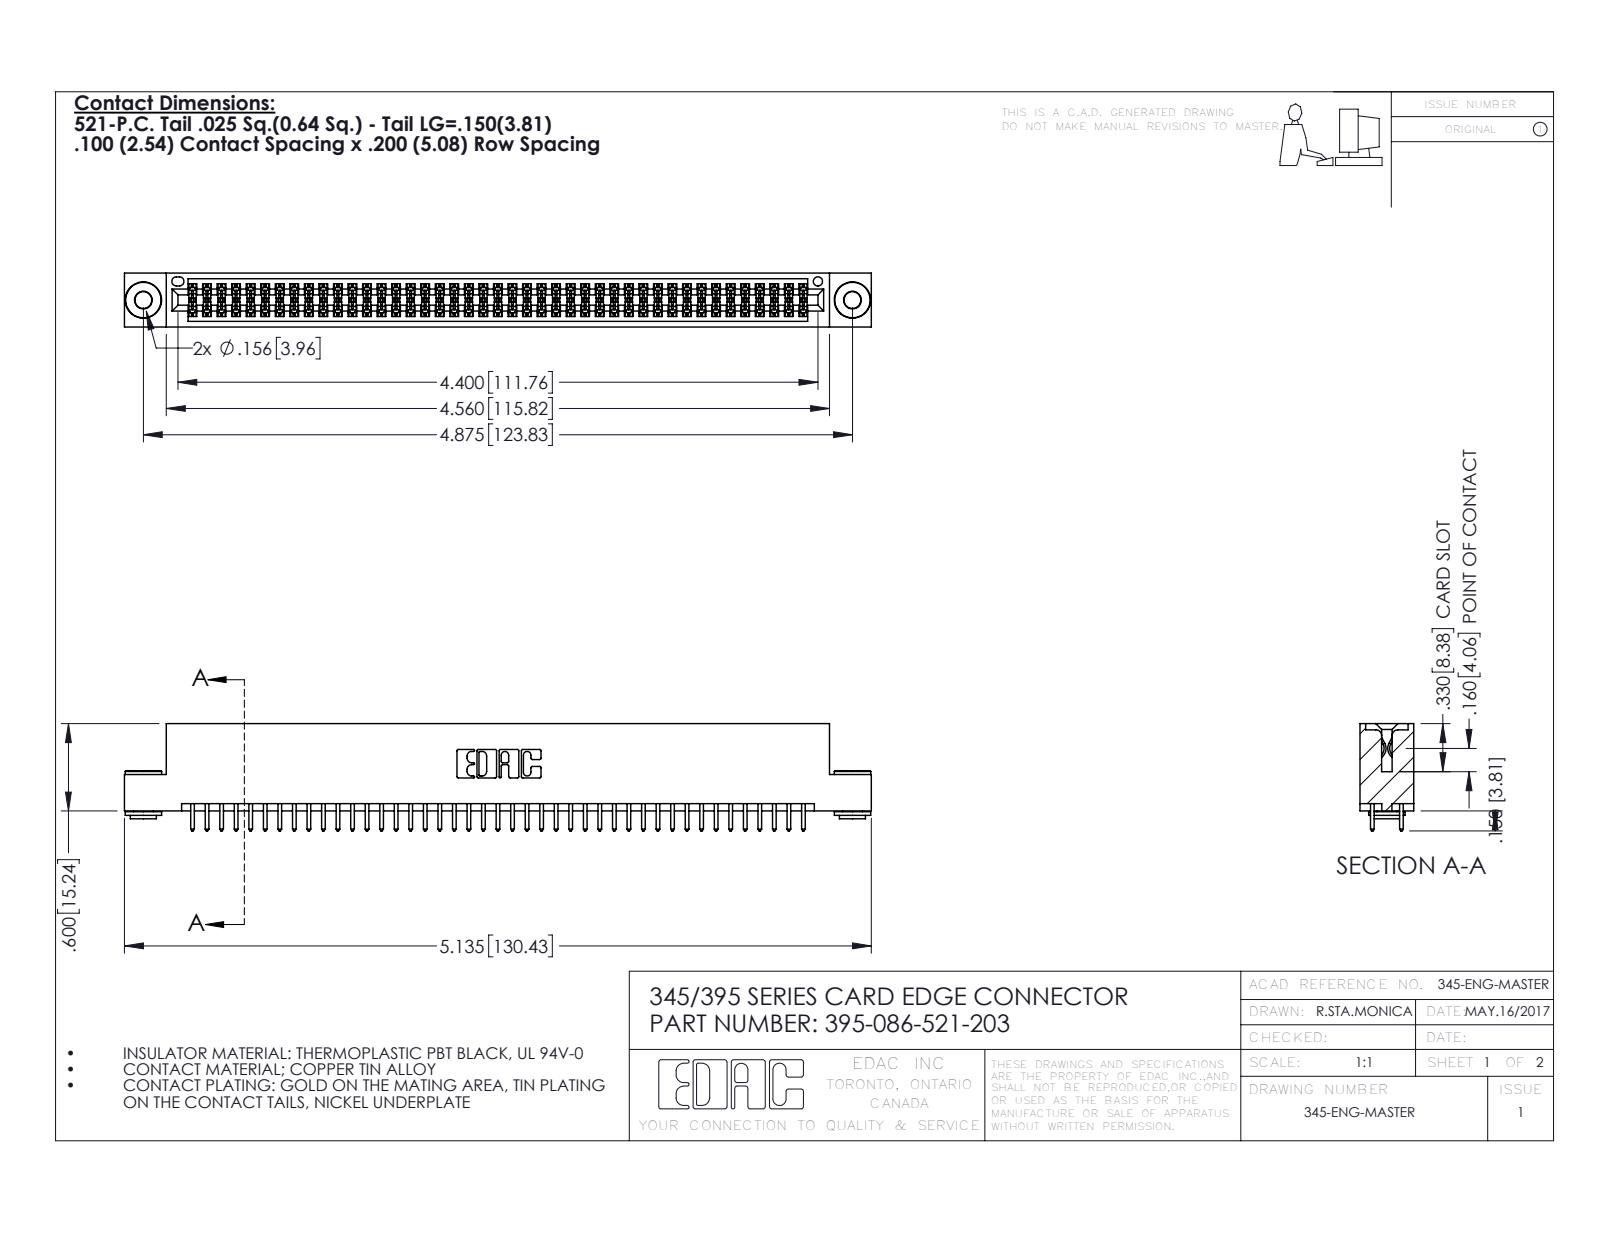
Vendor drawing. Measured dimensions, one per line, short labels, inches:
name: 345-250-002_345-250-002-102; 345-292-001_345-293-121; 395-086-521-203; 345 Part_Flush Mounting Lugs - 0.156 Dia-TH
written by: SolidWorks 2016 (CONFIG_CONTROL_DESIGN)
unit: in
bodies: 89 solids, 4464 faces (2928 planar, 1528 cylindrical, 8 other)
size: 5.135 × 0.737 × 0.37
volume: 0.773 in³; area: 29.01 in²
holes: 2× ⌀0.116, 2× ⌀0.156, 1× ⌀0.064
bosses: 2× ⌀0.25, 2× ⌀0.18, 2× ⌀0.136
rounds: 129× R0.006, 86× R0.01, 22× R0.01, 6× R0.007, 6× R0.031, 3× R0.026, 2× R0.014, 2× R0.019
face distances: 0.072, 0.298, 0.2, 0.025, 0.37, 0.098, 0.272, 0.225, 0.175, 0.149
hole spacings: 0.27, 4.639, 4.875
